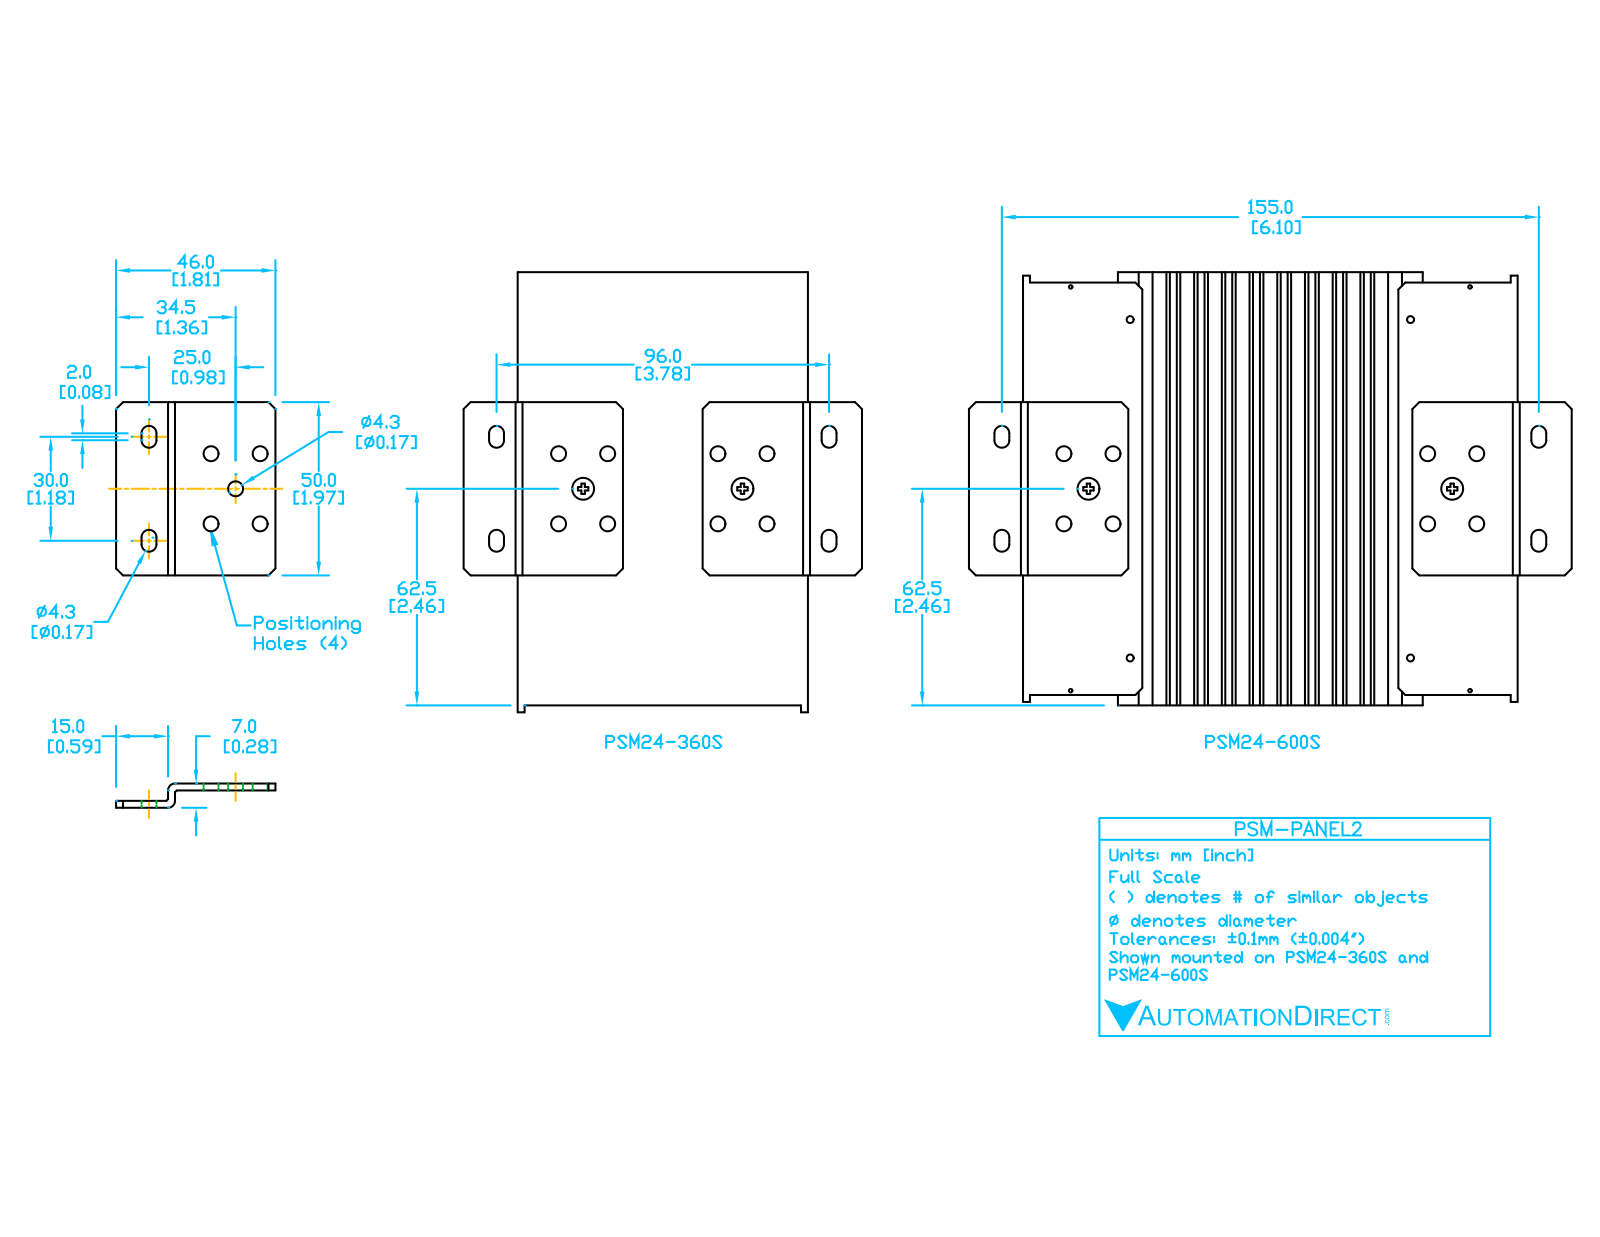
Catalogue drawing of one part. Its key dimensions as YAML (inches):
part_name: "PSM-PANEL2"
step_written_by: "SolidWorks 2011 (CONFIG_CONTROL_DESIGN)"
units: inches
bodies: {solids: 1, faces: 38, planar: 18, cylindrical: 20, other: 0}
overall_size: [1.97, 1.81, 0.28]
volume: 0.288
surface_area: 8.285
round_holes:
  - {diameter: 0.14, count: 4}
  - {diameter: 0.172, count: 1}
partial_cylinders:
  - {radius: 0.085, count: 4}
  - {radius: 0.02, count: 1}
  - {radius: 0.022, count: 1}
  - {radius: 0.098, count: 1}
  - {radius: 0.1, count: 1}
face_to_face_distances: [0.078, 0.202, 0.124, 0.28, 1.142, 1.22, 1.81, 0.668, 0.59, 1.97]
hole_center_spacings: [0.59, 0.7, 0.95, 1.18]
